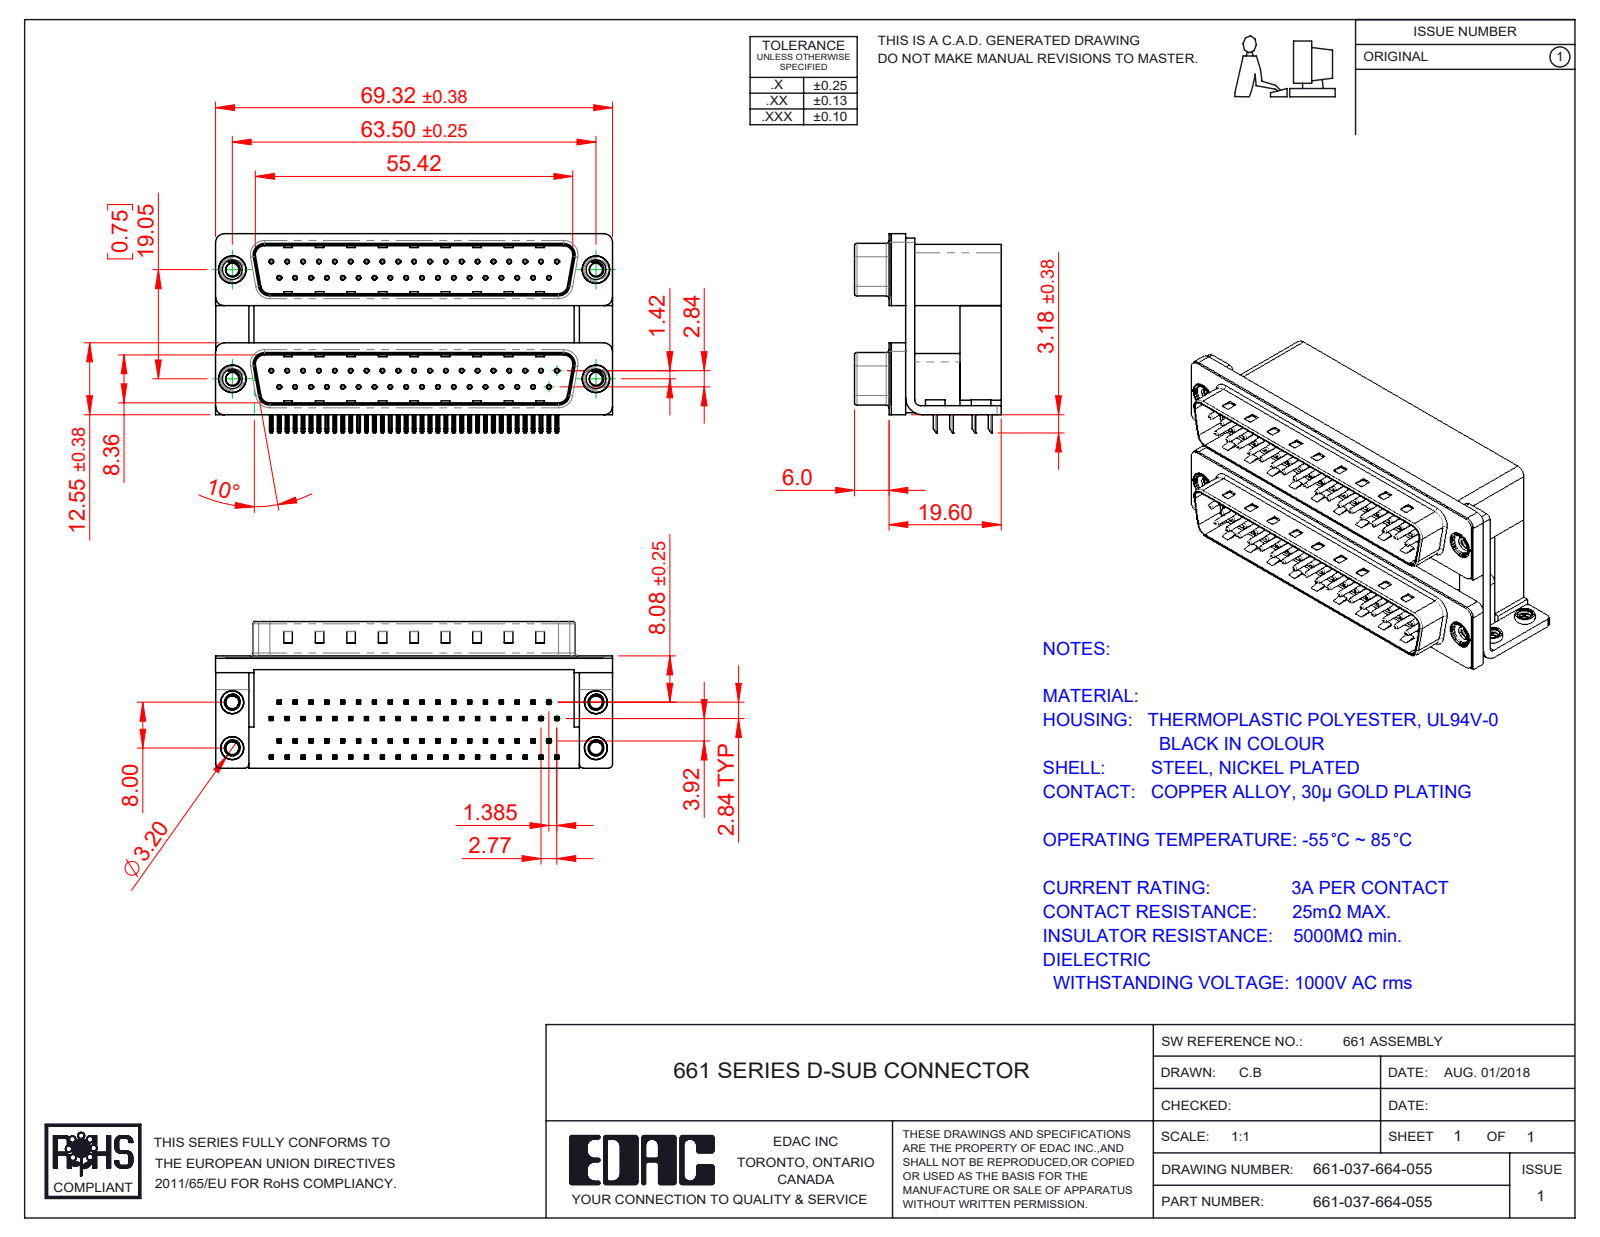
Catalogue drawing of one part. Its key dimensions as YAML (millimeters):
part_name: "661 Threaded Rivet_4-40; 661-037-664-055; 661 Contact Top Upper_M; 661 Contact Top Lower (+8 more)"
step_written_by: "SolidWorks 2020 (CONFIG_CONTROL_DESIGN)"
units: millimeters
bodies: {solids: 89, faces: 6722, planar: 4262, cylindrical: 1870, other: 590}
overall_size: [69.32, 34.78, 25.6]
volume: 29287
surface_area: 30012
round_holes:
  - {diameter: 0.35, count: 74}
  - {diameter: 0.8, count: 74}
  - {diameter: 2.26, count: 8}
  - {diameter: 2.75, count: 4}
  - {diameter: 3.2, count: 4}
  - {diameter: 3.5, count: 4}
  - {diameter: 4, count: 4}
  - {diameter: 4.8, count: 4}
  - {diameter: 5, count: 4}
round_bosses_or_shafts:
  - {diameter: 0.75, count: 74}
  - {diameter: 4.9, count: 4}
  - {diameter: 4.75, count: 4}
  - {diameter: 4, count: 4}
  - {diameter: 3.9, count: 4}
  - {diameter: 3.4, count: 4}
partial_cylinders:
  - {radius: 0.25, count: 296}
  - {radius: 0.12, count: 148}
  - {radius: 0.5, count: 16}
  - {radius: 1.5, count: 14}
  - {radius: 0.75, count: 8}
  - {radius: 0.9, count: 8}
  - {radius: 1.6, count: 8}
  - {radius: 2, count: 8}
face_to_face_distances: [19.05, 0.4, 19.2, 10.69, 7.2, 12, 8.36, 8.76, 18.7, 2.84]
hole_center_spacings: [2.77, 5.54, 3.16, 8.31, 11.08, 13.85, 16.62, 19.39]
